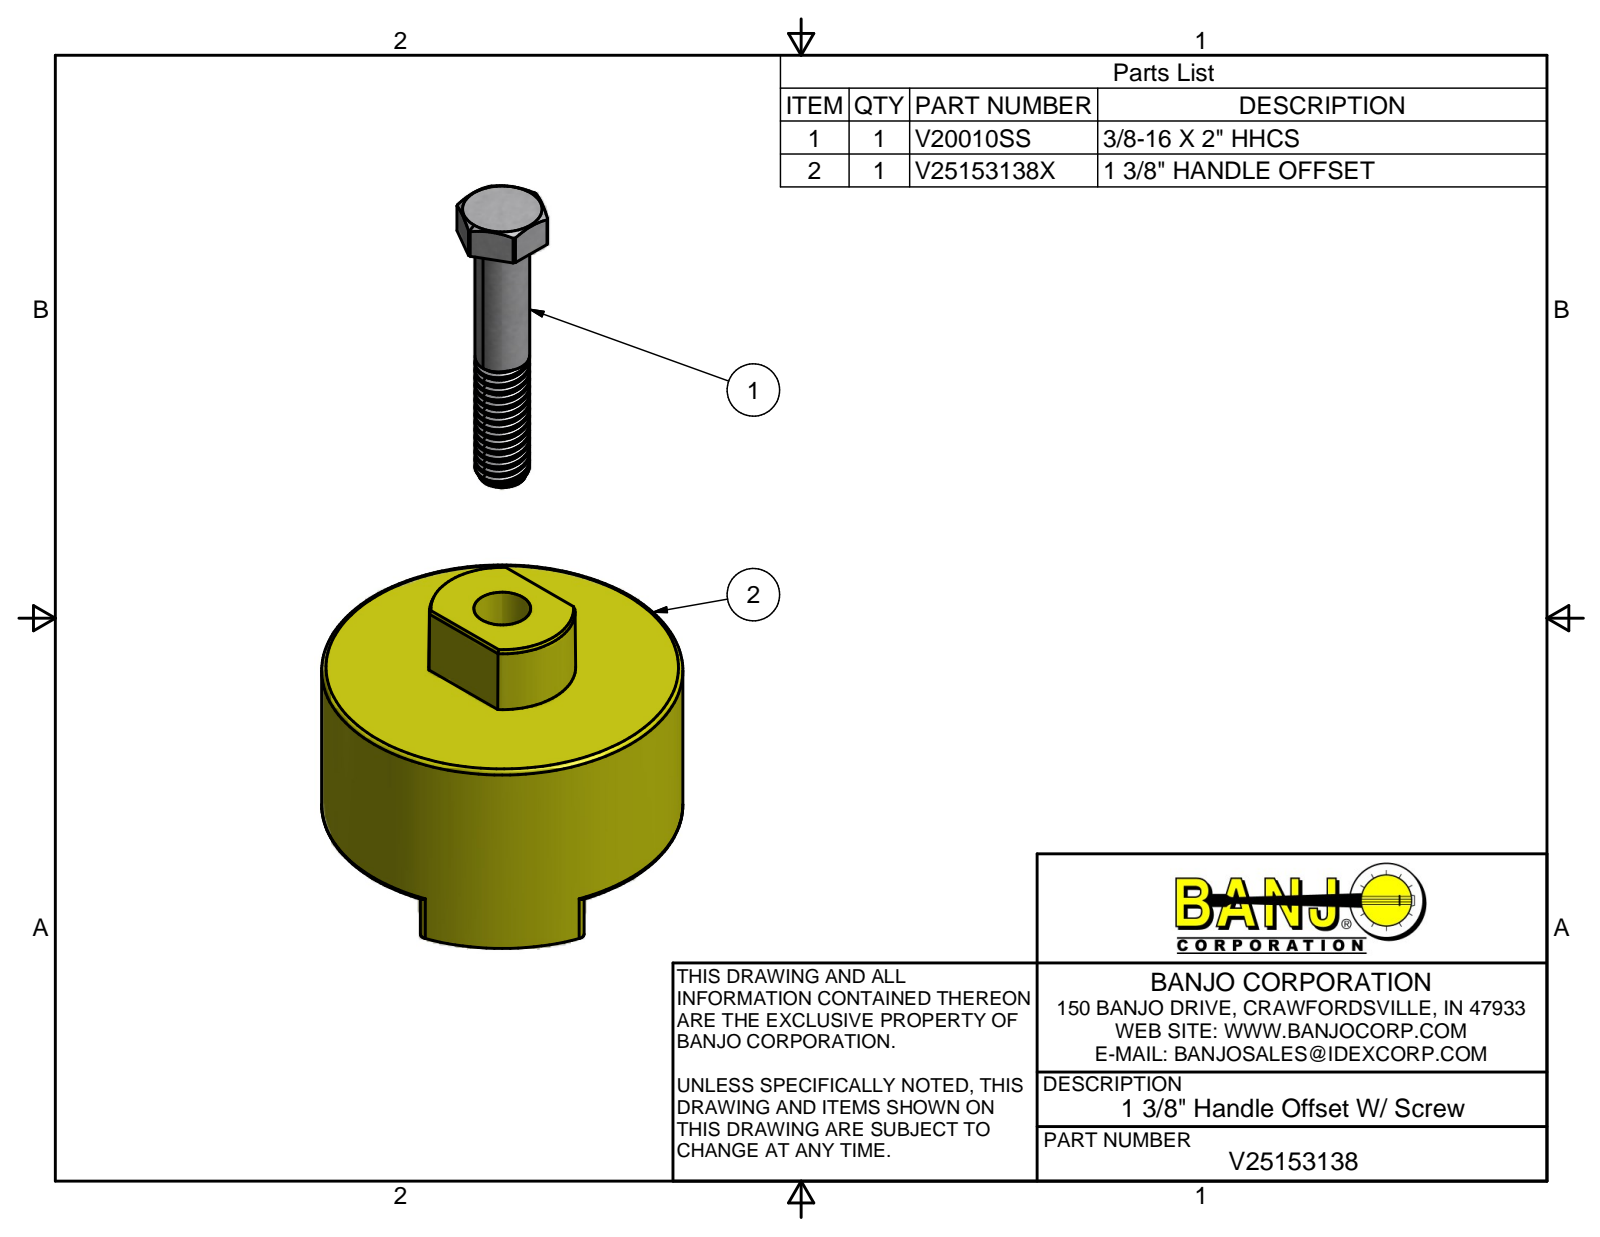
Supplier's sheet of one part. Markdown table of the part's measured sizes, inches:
| quantity | value |
| --- | --- |
| part name | DRAWING3 |
| STEP written by | Mechanical Desktop 2009 (CONFIG_CONTROL_DESIGN) |
| units | inches |
| bodies | 2 solids, 141 faces (33 planar, 28 cylindrical, 80 other) |
| overall size | 4.62 × 2.48 × 2.48 |
| volume | 4.731 in³ |
| surface area | 39.01 in² |
| round holes (diameter × count) | 0.39 × 1 |
| round bosses / shafts (diameter × count) | 2.48 × 1, 0.375 × 1 |
| partial cylindrical surfaces (radius × count) | 0.06 × 12, 0.03 × 4, 0.504 × 1, 0.77 × 1, 1.115 × 1 |
| main face-to-face distances | 1.375, 1.25, 0.125, 0.5, 0.037, 0.718, 0.68, 0.75, 0.875, 1.87 |
